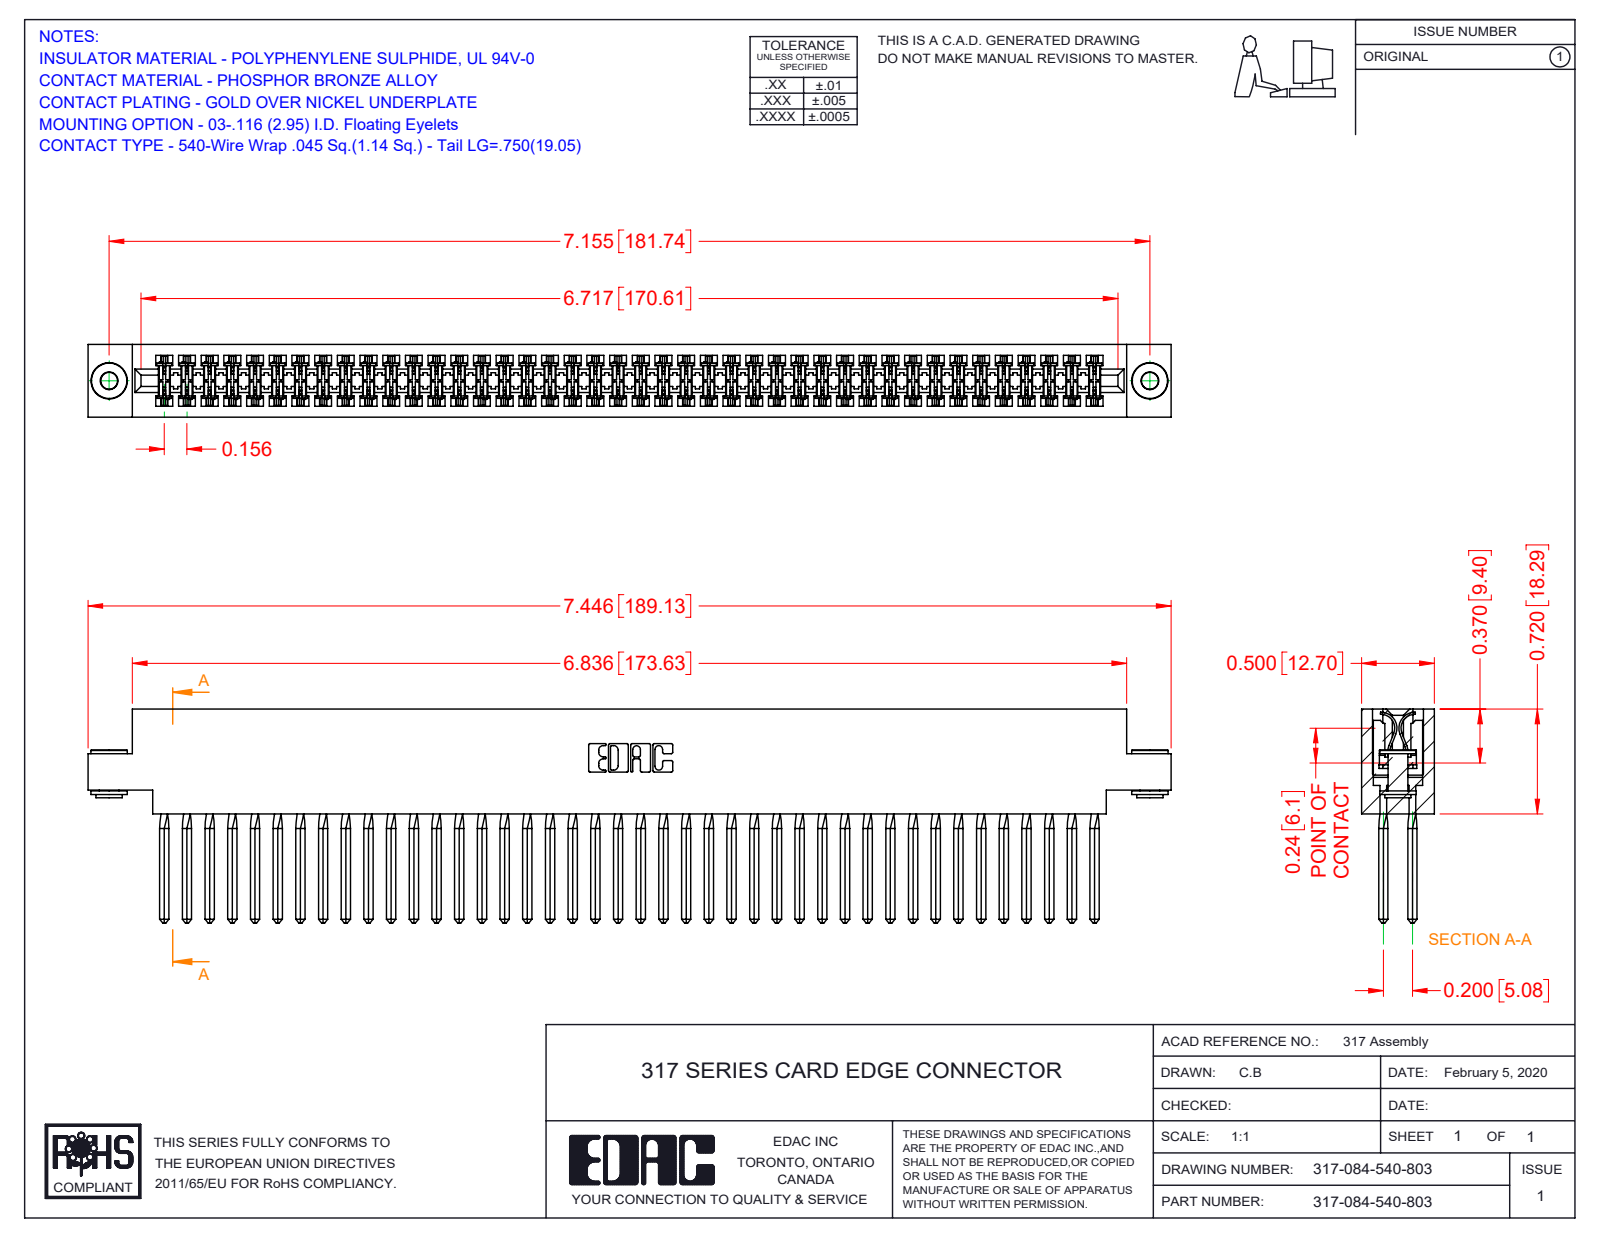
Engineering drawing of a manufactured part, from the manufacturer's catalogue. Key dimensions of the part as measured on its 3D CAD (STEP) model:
Part name (STEP PRODUCT): 345-250-002_345-250-002-102; 317-084-540-803; 317-290-001_540; 317 Part_.156 Dia - TH
STEP written by: SolidWorks 2016 (CONFIG_CONTROL_DESIGN)
Units: inches
Bodies: 87 solids, 7616 faces (6200 planar, 1072 cylindrical, 344 other)
Overall size (bounding box): 7.446 × 1.47 × 0.5
Volume: 1.938 in³ · Surface area: 73.73 in²
Round holes (diameter × count): ⌀0.116 ×2, ⌀0.156 ×2
Round bosses / shafts (diameter × count): ⌀0.25 ×2, ⌀0.18 ×2, ⌀0.136 ×2
Partial cylindrical surfaces — rounded edges, fillets, slot ends (radius × count): R0.015 ×168, R0.01 ×22, R0.007 ×6, R0.031 ×6, R0.026 ×3, R0.095 ×2, R0.1 ×2, R0.11 ×2
Main face-to-face distances: 0.5, 0.075, 0.425, 0.35, 0.195, 0.094, 0.2, 0.115, 0.131, 0.046
Hole centre spacings: 7.155
